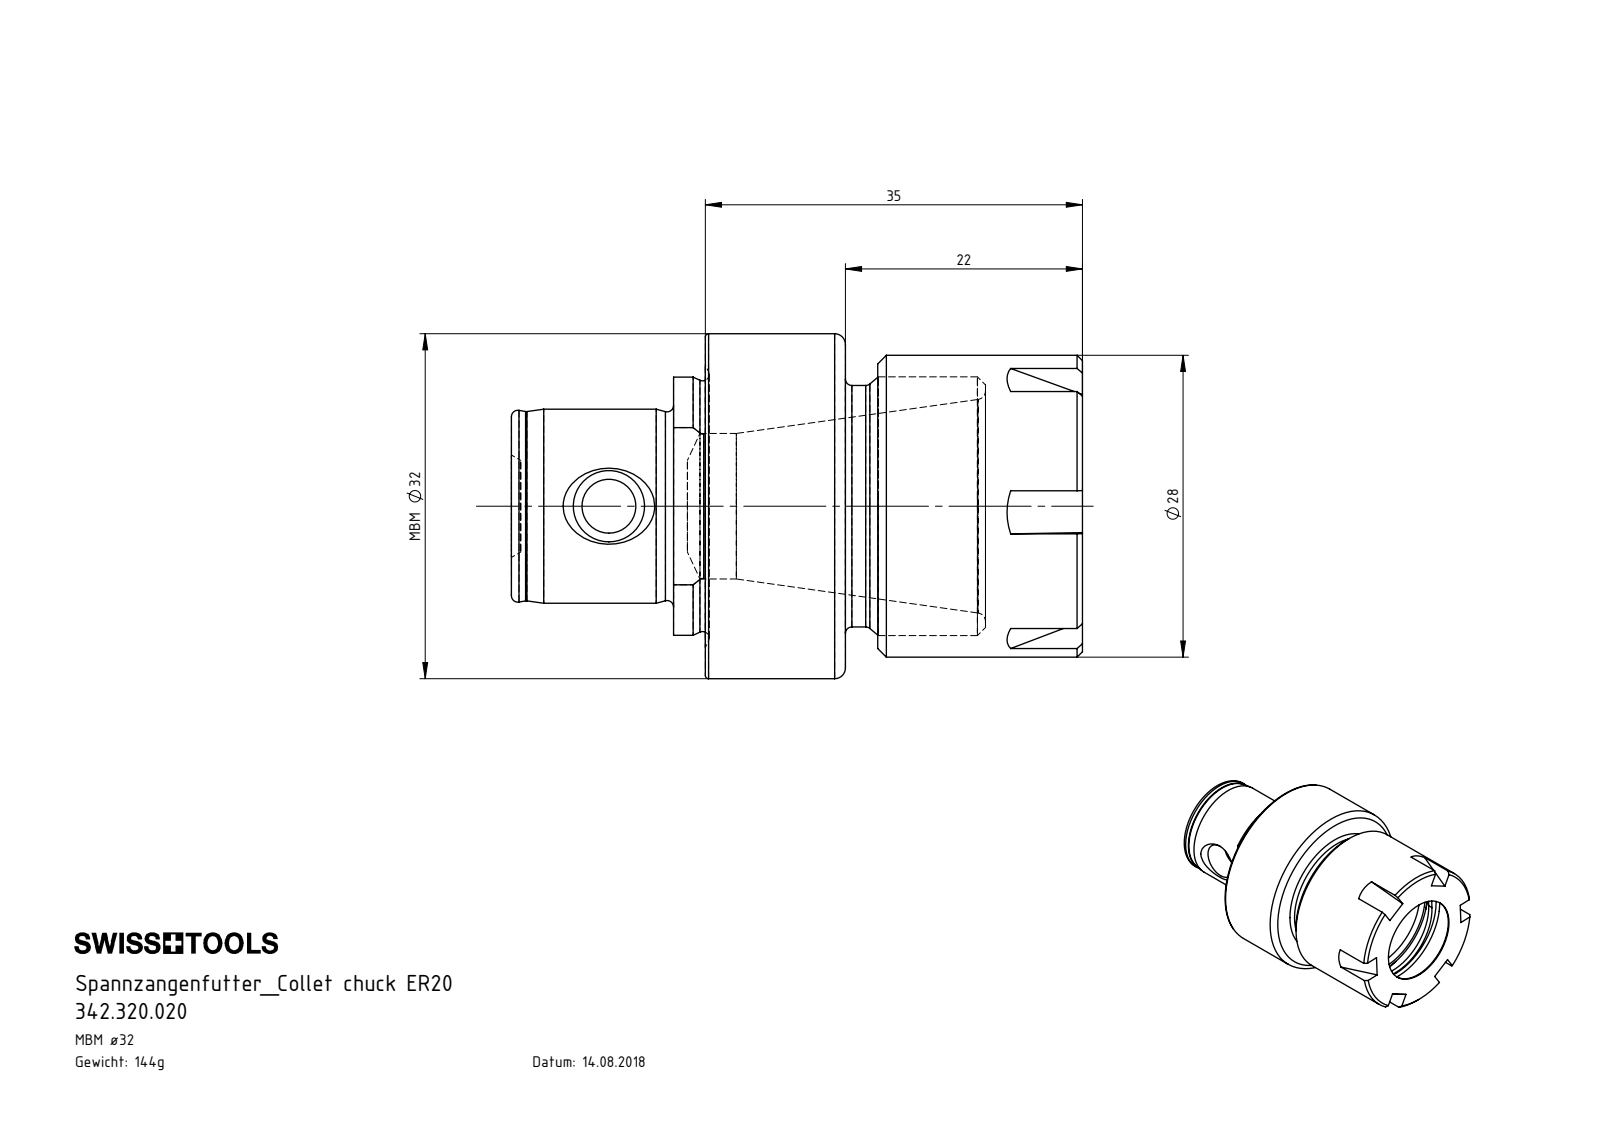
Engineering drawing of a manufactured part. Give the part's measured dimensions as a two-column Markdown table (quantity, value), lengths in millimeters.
| quantity | value |
| --- | --- |
| part name | MB3-E21.K01.035_C; E21-ER1.001.019; MB3.E21.K01.035 |
| STEP written by | SolidWorks 2017 (AUTOMOTIVE_DESIGN) |
| units | millimeters |
| bodies | 2 solids, 81 faces (33 planar, 15 cylindrical, 33 other) |
| overall size | 53 × 32 × 32 |
| volume | 18 325 mm³ |
| surface area | 10 323 mm² |
| round holes (diameter × count) | 5 × 1, 8.5 × 1, 13.5 × 1, 15.9 × 1, 23 × 1, 25 × 1 |
| round bosses / shafts (diameter × count) | 32 × 1, 28 × 1, 24 × 1, 22.4 × 1, 18 × 1 |
| partial cylindrical surfaces (radius × count) | 9.6 × 2, 11.97 × 1 |
| main face-to-face distances | 13, 22, 35, 19, 18, 31, 53, 34, 16, 3 |
